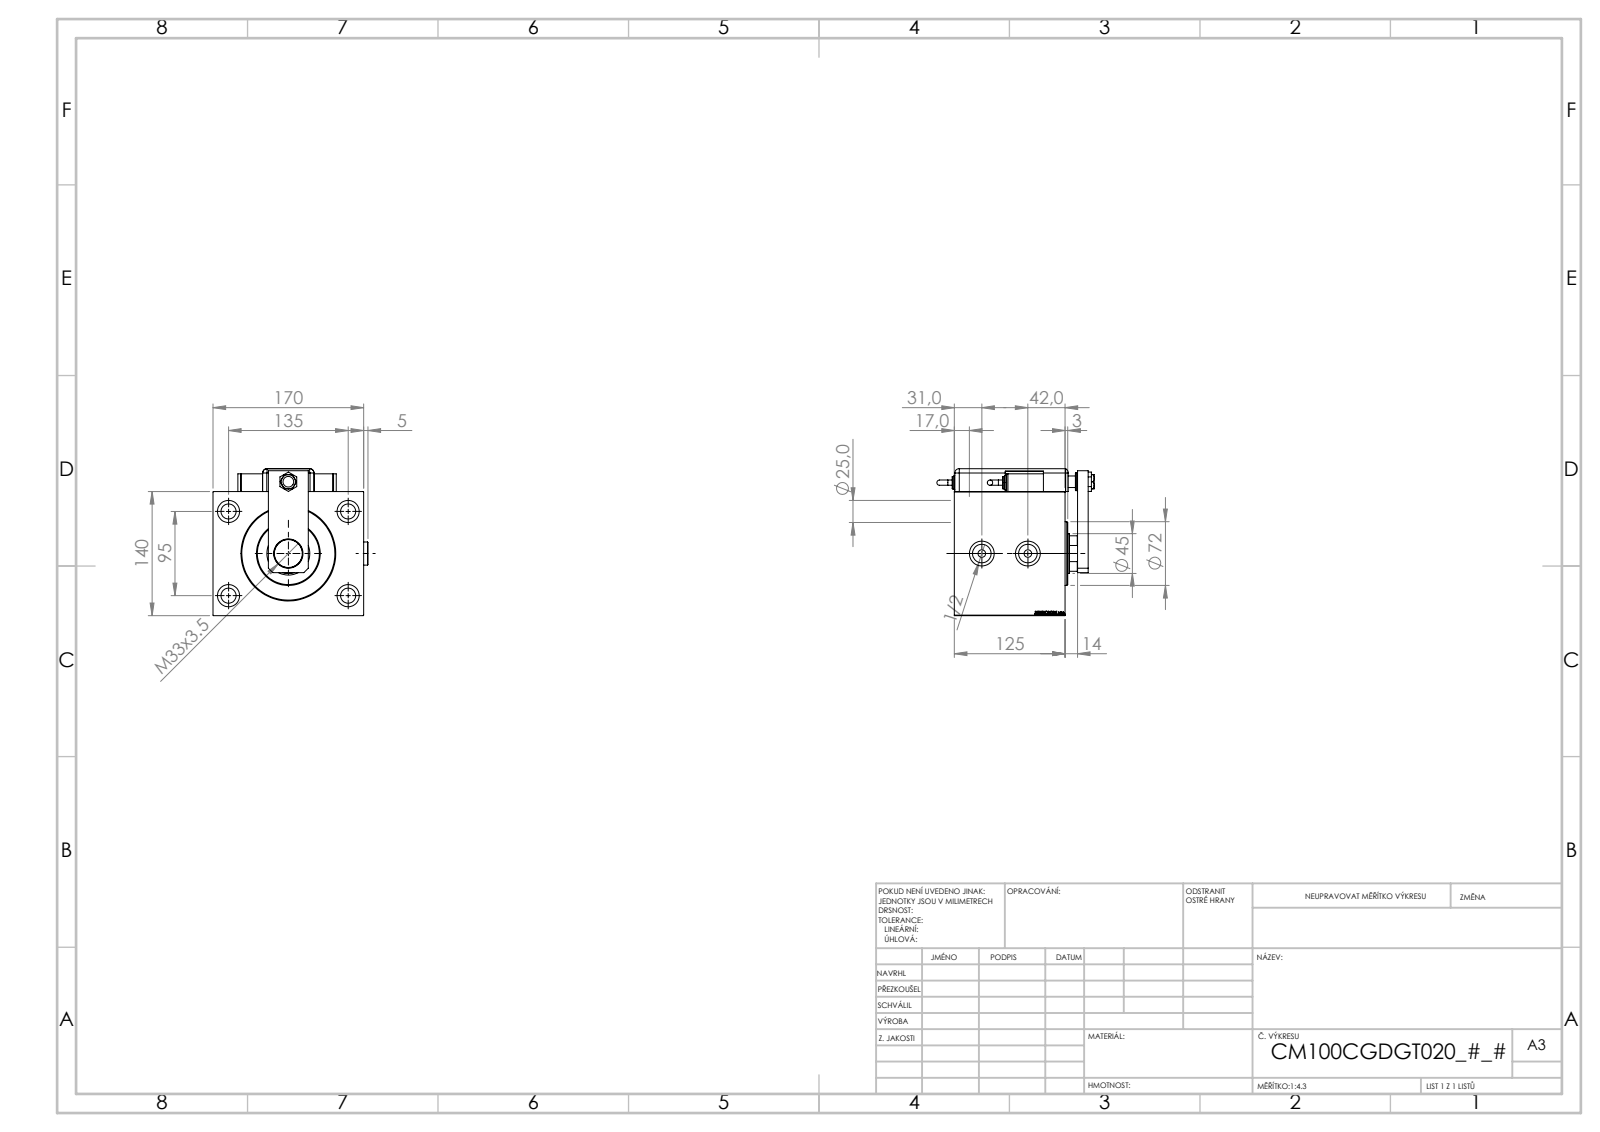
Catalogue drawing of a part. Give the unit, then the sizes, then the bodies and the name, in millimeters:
Units: millimetres
Overall size (bounding box): 177.66 × 174.9 × 165.8
Round holes (diameter × count): ⌀17 ×4, ⌀25 ×4, ⌀4 ×2, ⌀8 ×2, ⌀8.5 ×2, ⌀20.96 ×2, ⌀28 ×2, ⌀12 ×1, ⌀13 ×1, ⌀14 ×1, ⌀31.5 ×1, ⌀33 ×1
Round bosses / shafts (diameter × count): ⌀20 ×3, ⌀26 ×2, ⌀16 ×2, ⌀14 ×2, ⌀6 ×2, ⌀72 ×1
Partial cylindrical surfaces — rounded edges, fillets, slot ends (radius × count): R5 ×9, R10 ×1, R22 ×1
Main face-to-face distances: 140, 125, 170, 51, 74, 3, 10, 21.6, 29.4, 103.4
Hole centre spacings: 82.54, 75.36, 95, 135, 145.15, 165.08, 20, 52
Volume: 2 923 000 mm³ · Surface area: 306 197 mm²
Bodies: 15 solids, 1301 faces (649 planar, 131 cylindrical, 521 other)
Part name (STEP PRODUCT): V450CM_C_Body; Zatka_OIL_PORT; SWITCH_Q_FRONT_BACK; SWITCH Q (+7 more)
STEP written by: SolidWorks 2019 (CONFIG_CONTROL_DESIGN)
